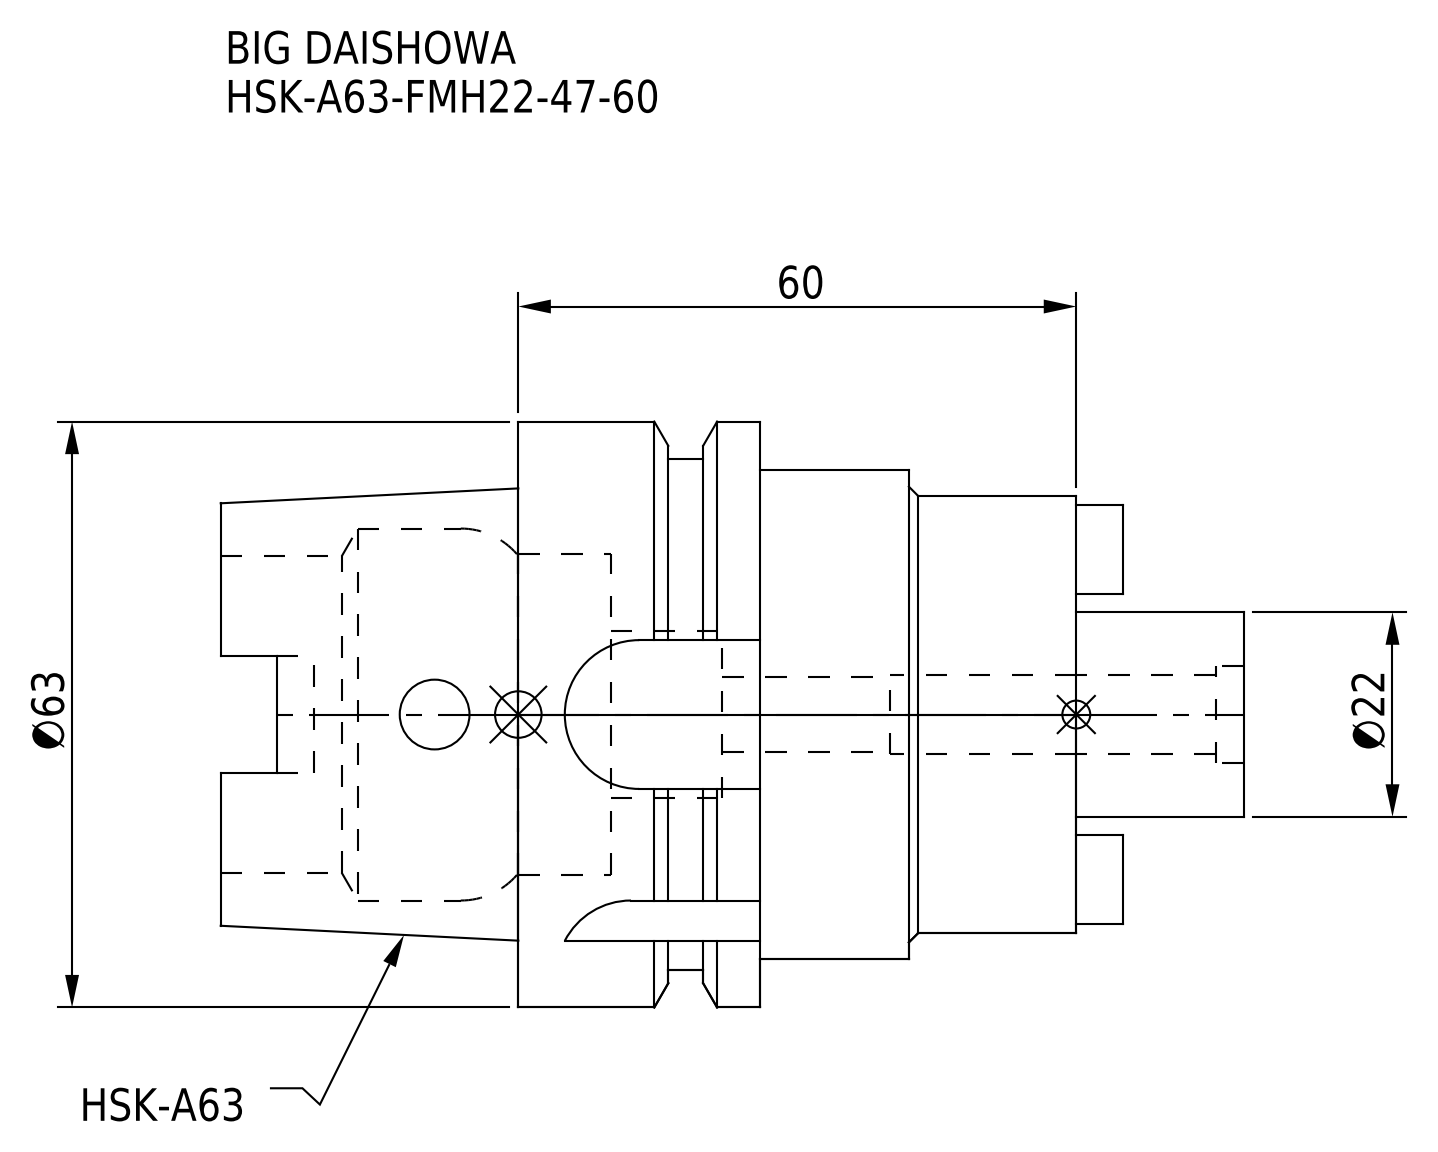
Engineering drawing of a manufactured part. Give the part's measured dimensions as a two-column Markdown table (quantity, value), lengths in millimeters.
| quantity | value |
| --- | --- |
| part name | HSK-A63-FMH22-47-60 |
| STEP written by | CREO PARAMETRIC BY PTC INC, 2016380 (AUTOMOTIVE_DESIGN) |
| units | millimeters |
| bodies | 1 solid, 97 faces (45 planar, 38 cylindrical, 14 other) |
| overall size | 110 × 63 × 63 |
| volume | 152 719 mm³ |
| surface area | 30 680 mm² |
| round holes (diameter × count) | 7.5 × 1, 8 × 1, 8.5 × 1, 10.5 × 1, 18 × 1, 34 × 1, 34.5 × 1, 40 × 1 |
| round bosses / shafts (diameter × count) | 63 × 1, 55 × 1, 52.6 × 1, 47 × 1, 22 × 1 |
| partial cylindrical surfaces (radius × count) | 8 × 2, 9 × 1 |
| main face-to-face distances | 60, 26, 34, 50.05, 16.05, 9.95, 18, 92, 58, 41.95 |
